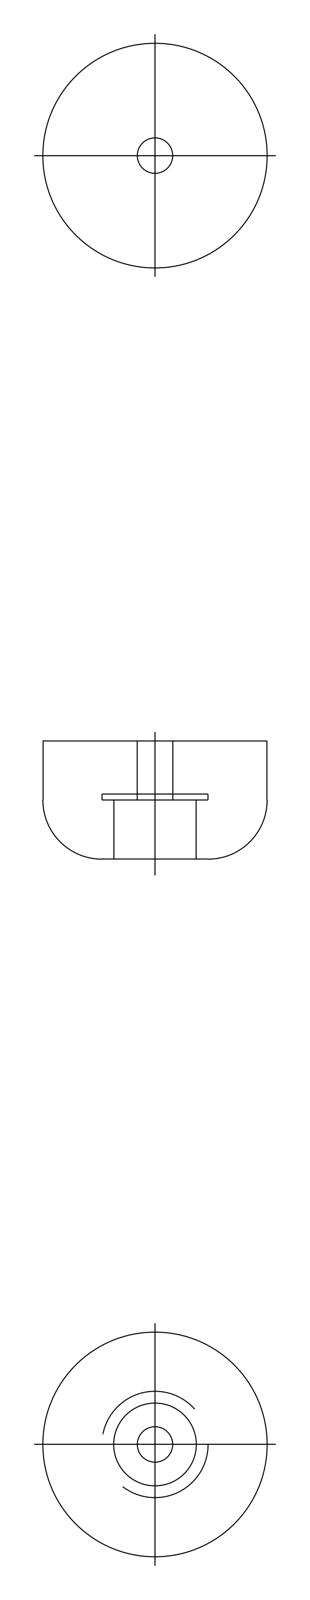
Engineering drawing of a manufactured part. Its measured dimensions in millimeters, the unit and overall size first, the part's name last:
Units: millimetres
Overall size (bounding box): 19 × 19 × 10
Round holes (diameter × count): ⌀3 ×1, ⌀7 ×1, ⌀9 ×1
Round bosses / shafts (diameter × count): ⌀19 ×1
Main face-to-face distances: 4.5, 5, 0.5, 5.5, 10
Volume: 2 325 mm³ · Surface area: 1 359 mm²
Bodies: 2 solids, 20 faces (6 planar, 12 cylindrical, 2 other)
Part name (STEP PRODUCT): washer; rubber foot
STEP written by: spGate 15.6.1 (AUTOMOTIVE_DESIGN)
